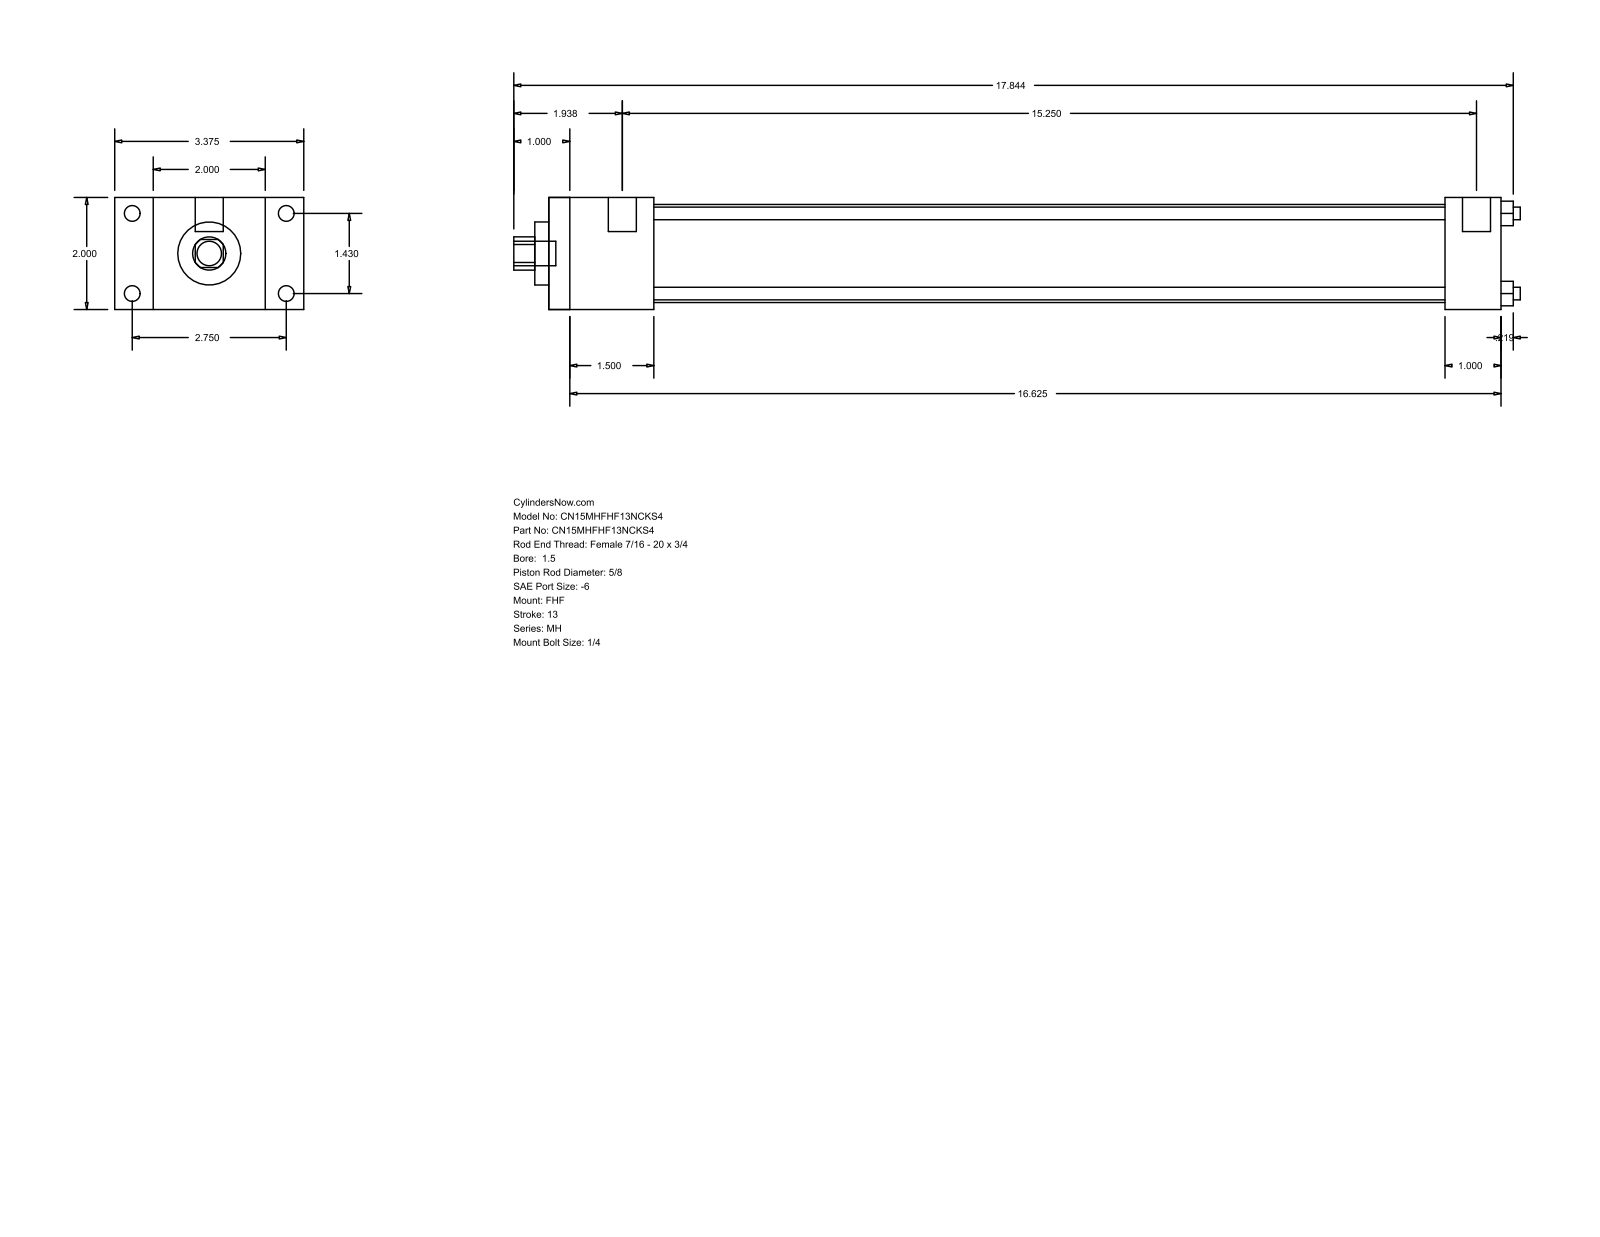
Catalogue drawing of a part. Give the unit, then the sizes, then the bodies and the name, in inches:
Units: inches
Overall size (bounding box): 17.969 × 3.375 × 2
Round holes (diameter × count): ⌀0.225 ×4, ⌀0.625 ×1, ⌀1.125 ×1, ⌀1.75 ×1
Round bosses / shafts (diameter × count): ⌀0.281 ×4, ⌀0.219 ×4, ⌀0.5 ×2, ⌀0.437 ×1
Partial cylindrical surfaces — rounded edges, fillets, slot ends (radius × count): R0.297 ×1
Main face-to-face distances: 2, 0.687, 2.687, 1.875, 3.375, 17, 15.125, 16, 14.125, 1
Hole centre spacings: 1.011, 1.43, 2.022
Bodies: 0 solids, 88 faces (60 planar, 28 cylindrical, 0 other)
Part name (STEP PRODUCT): MH_FHF__0150_0.625
STEP written by: GSSL Pune (CONFIG_CONTROL_DESIGN)
